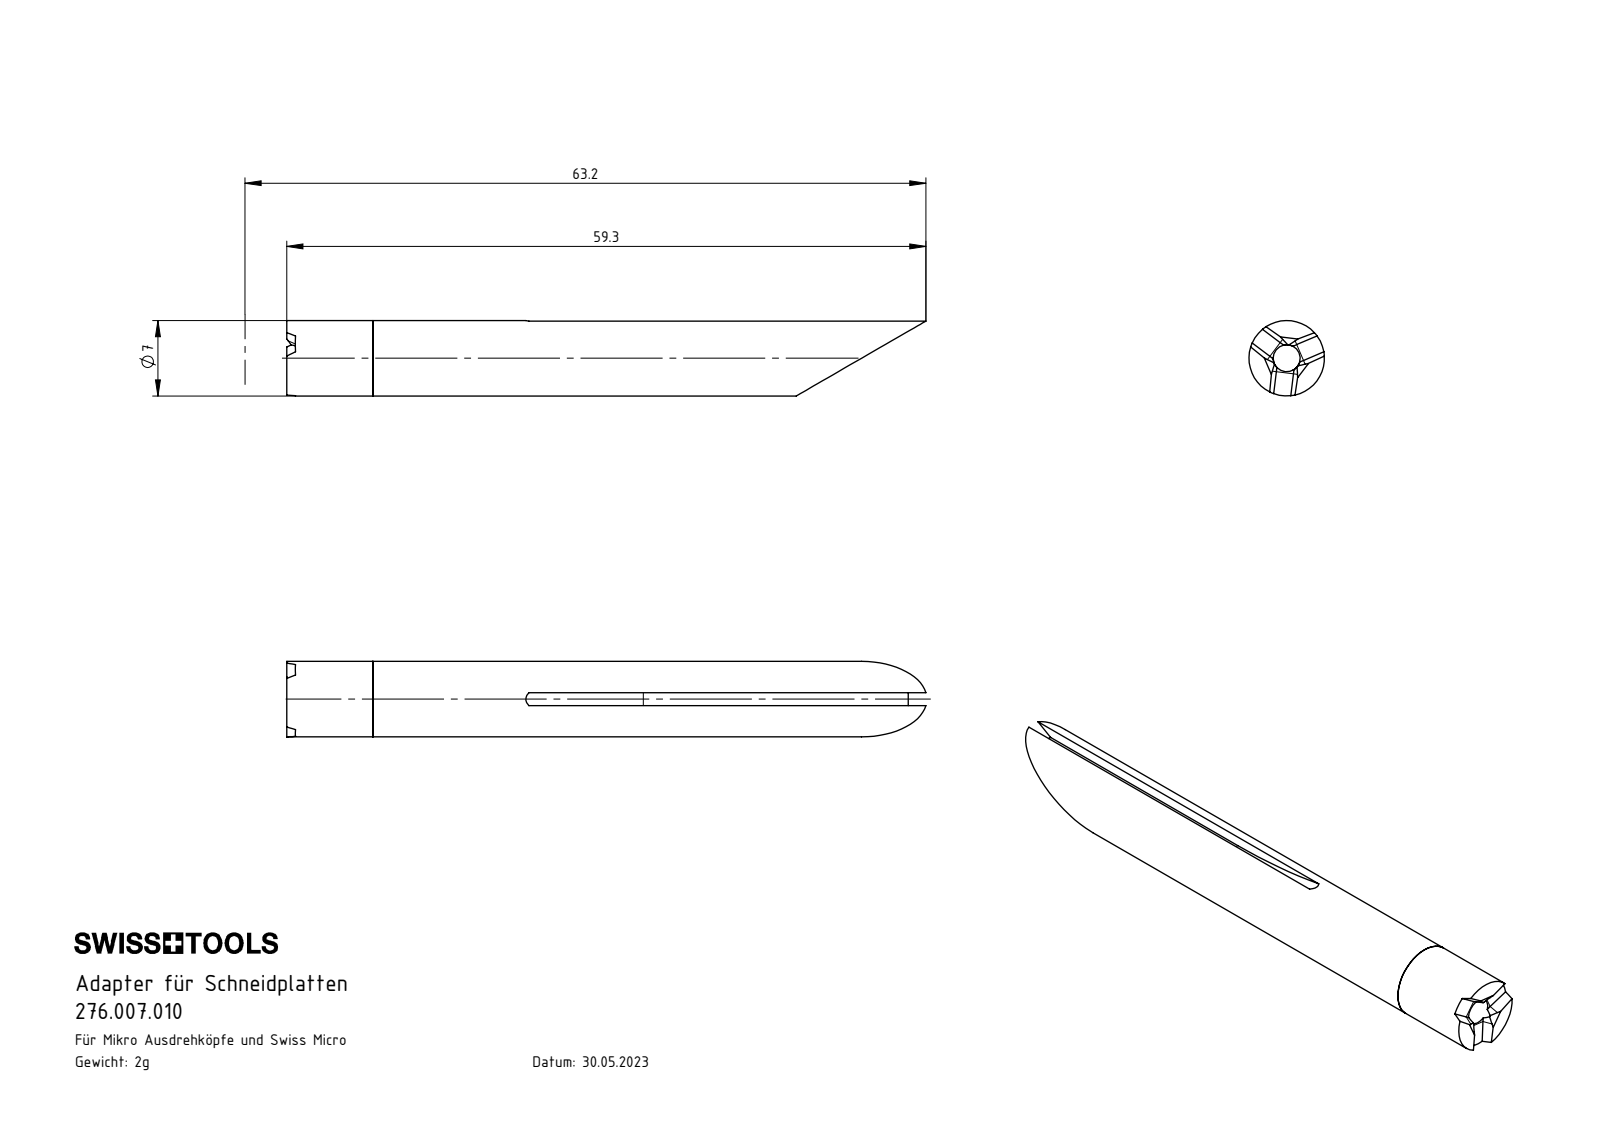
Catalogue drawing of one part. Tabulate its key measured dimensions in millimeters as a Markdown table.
| quantity | value |
| --- | --- |
| part name | D10.A07.35 HM_2; 276.007.010; D10.A07.35 HM |
| STEP written by | SolidWorks 2022 (CONFIG_CONTROL_DESIGN) |
| units | millimeters |
| bodies | 2 solids, 41 faces (18 planar, 15 cylindrical, 8 other) |
| overall size | 59.32 × 7 × 7 |
| volume | 1 959 mm³ |
| surface area | 1 477 mm² |
| round holes (diameter × count) | 2.5 × 1 |
| round bosses / shafts (diameter × count) | 7 × 1 |
| partial cylindrical surfaces (radius × count) | 4.9 × 3, 60 × 1 |
| main face-to-face distances | 1.2, 8 |
